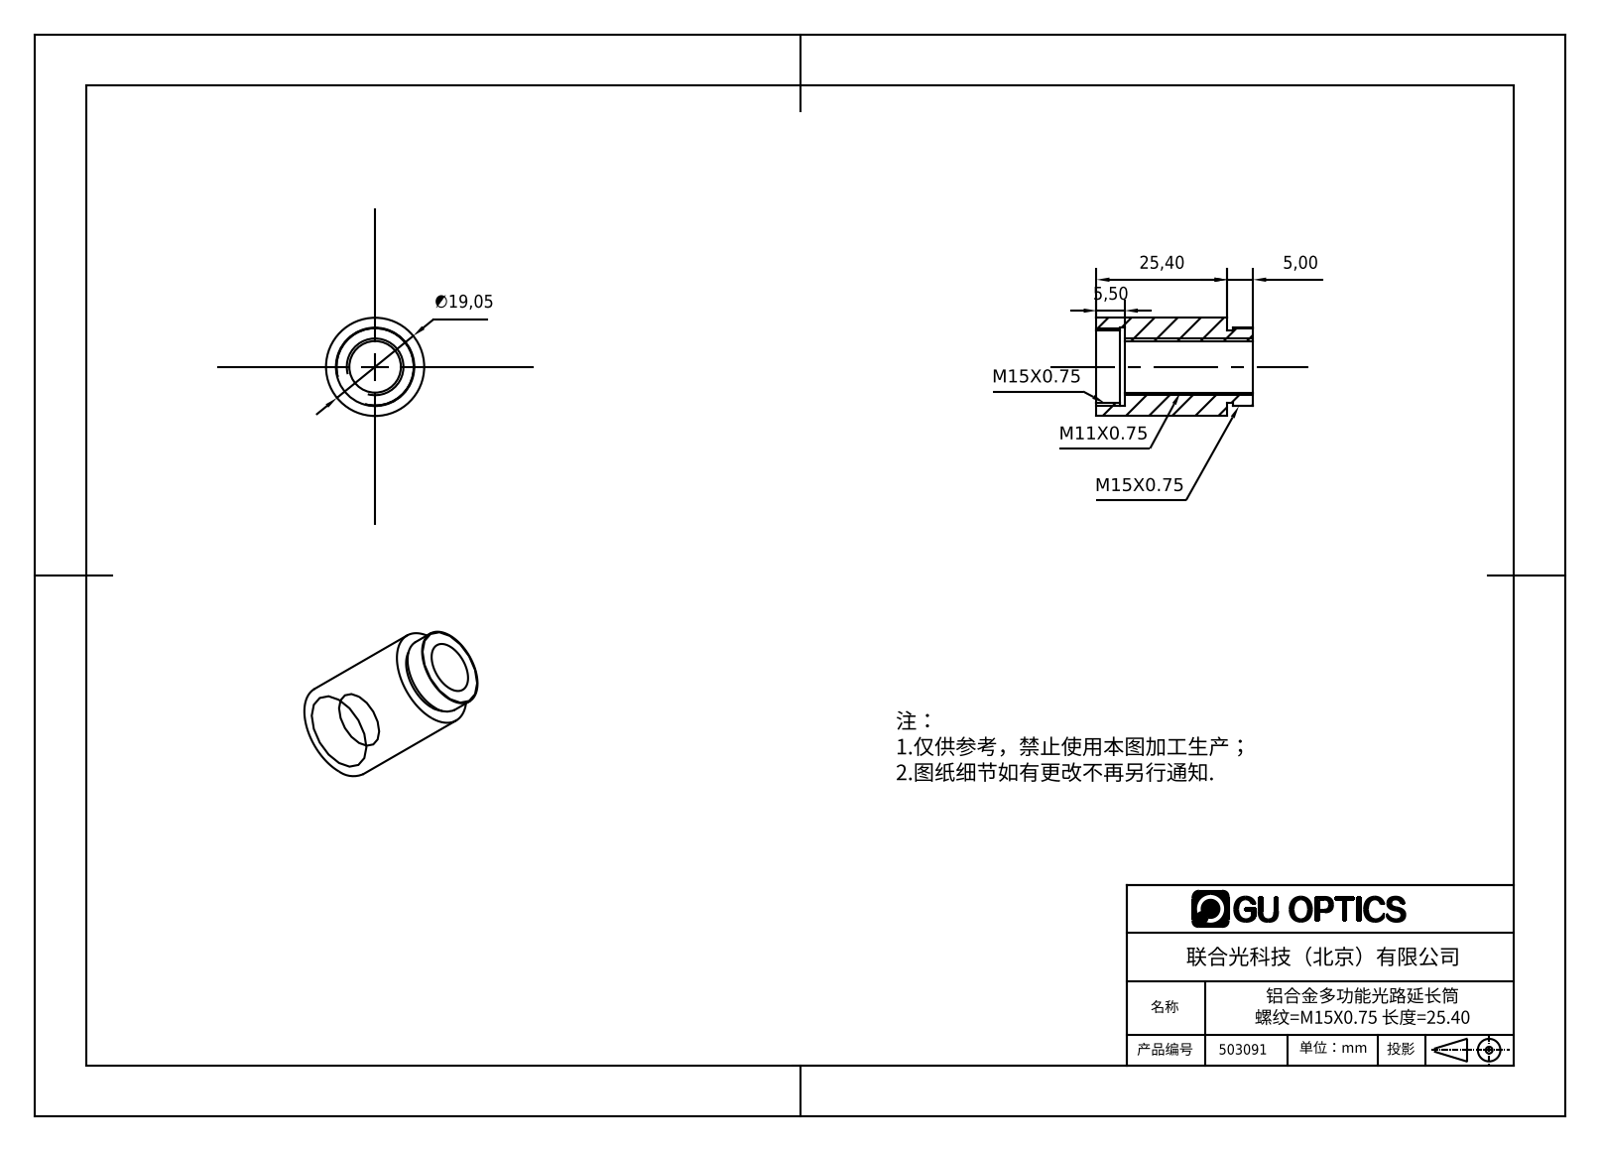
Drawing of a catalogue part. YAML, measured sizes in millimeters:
part_name: "503091"
step_written_by: "SolidWorks 2016 (AUTOMOTIVE_DESIGN)"
units: millimeters
bodies: {solids: 1, faces: 18, planar: 6, cylindrical: 12, other: 0}
overall_size: [30.4, 19.05, 19.05]
volume: 5290
surface_area: 3306
round_holes:
  - {diameter: 10, count: 1}
  - {diameter: 14, count: 1}
  - {diameter: 15.2, count: 1}
round_bosses_or_shafts:
  - {diameter: 19.05, count: 1}
face_to_face_distances: [25.4, 5.5, 19.9, 30.4, 24.9, 5, 1, 20.9, 26.4, 4]
